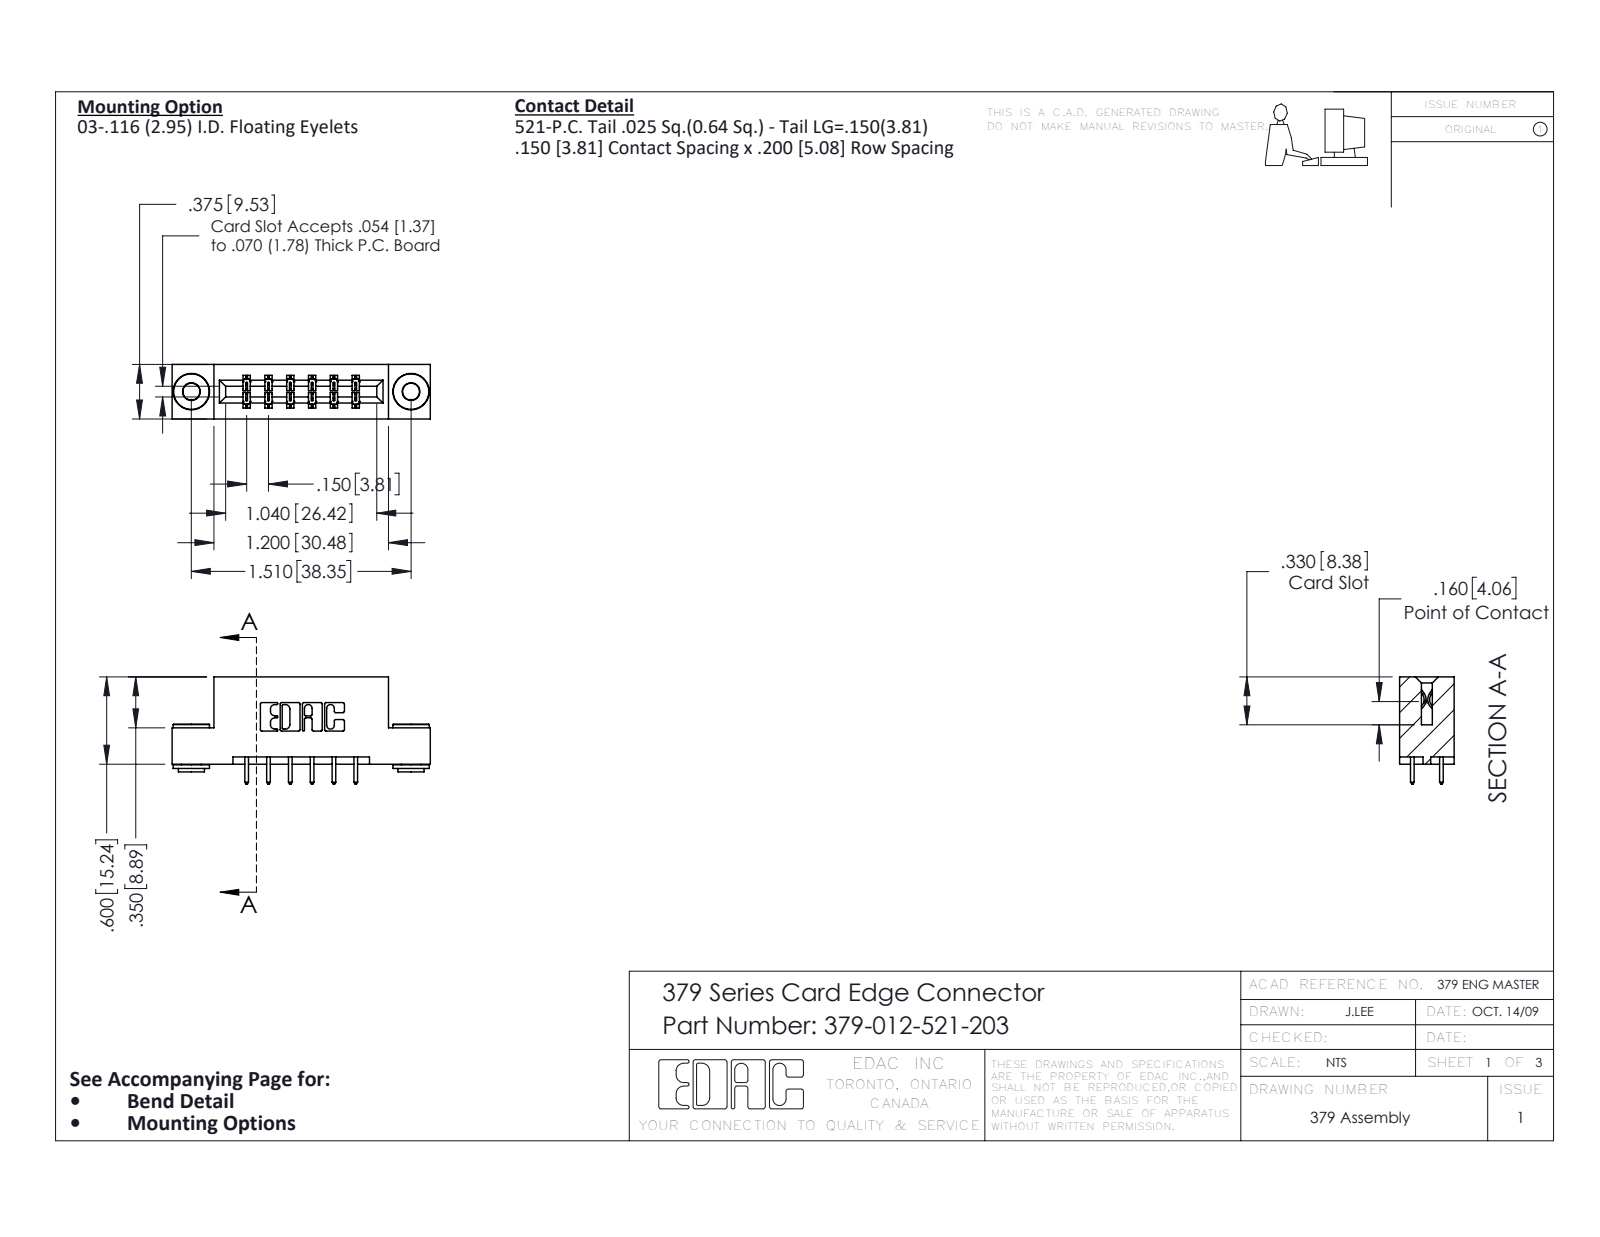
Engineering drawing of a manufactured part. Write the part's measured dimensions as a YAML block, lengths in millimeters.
part_name: "379-012-521-203; 379 Part_Flush - .156 Dia - TH; 345-292-001_345-293-121; 345-250-002_345-250-002-102"
step_written_by: "SolidWorks 2016 (CONFIG_CONTROL_DESIGN)"
units: millimeters
bodies: {solids: 15, faces: 776, planar: 512, cylindrical: 256, other: 8}
overall_size: [45.1, 18.7, 9.5]
volume: 4360
surface_area: 4757
round_holes:
  - {diameter: 2.9, count: 2}
  - {diameter: 4, count: 2}
round_bosses_or_shafts:
  - {diameter: 6.4, count: 2}
  - {diameter: 4.6, count: 2}
  - {diameter: 3.5, count: 2}
partial_cylinders:
  - {radius: 0.3, count: 22}
  - {radius: 0.2, count: 18}
  - {radius: 0.3, count: 12}
  - {radius: 0.2, count: 6}
  - {radius: 0.8, count: 6}
  - {radius: 0.7, count: 3}
  - {radius: 0.4, count: 2}
  - {radius: 0.6, count: 2}
face_to_face_distances: [7.6, 5.1, 1.3, 3.8, 9.5, 6.4, 8.9, 2.5, 1.9, 14]
hole_center_spacings: [38.4]
